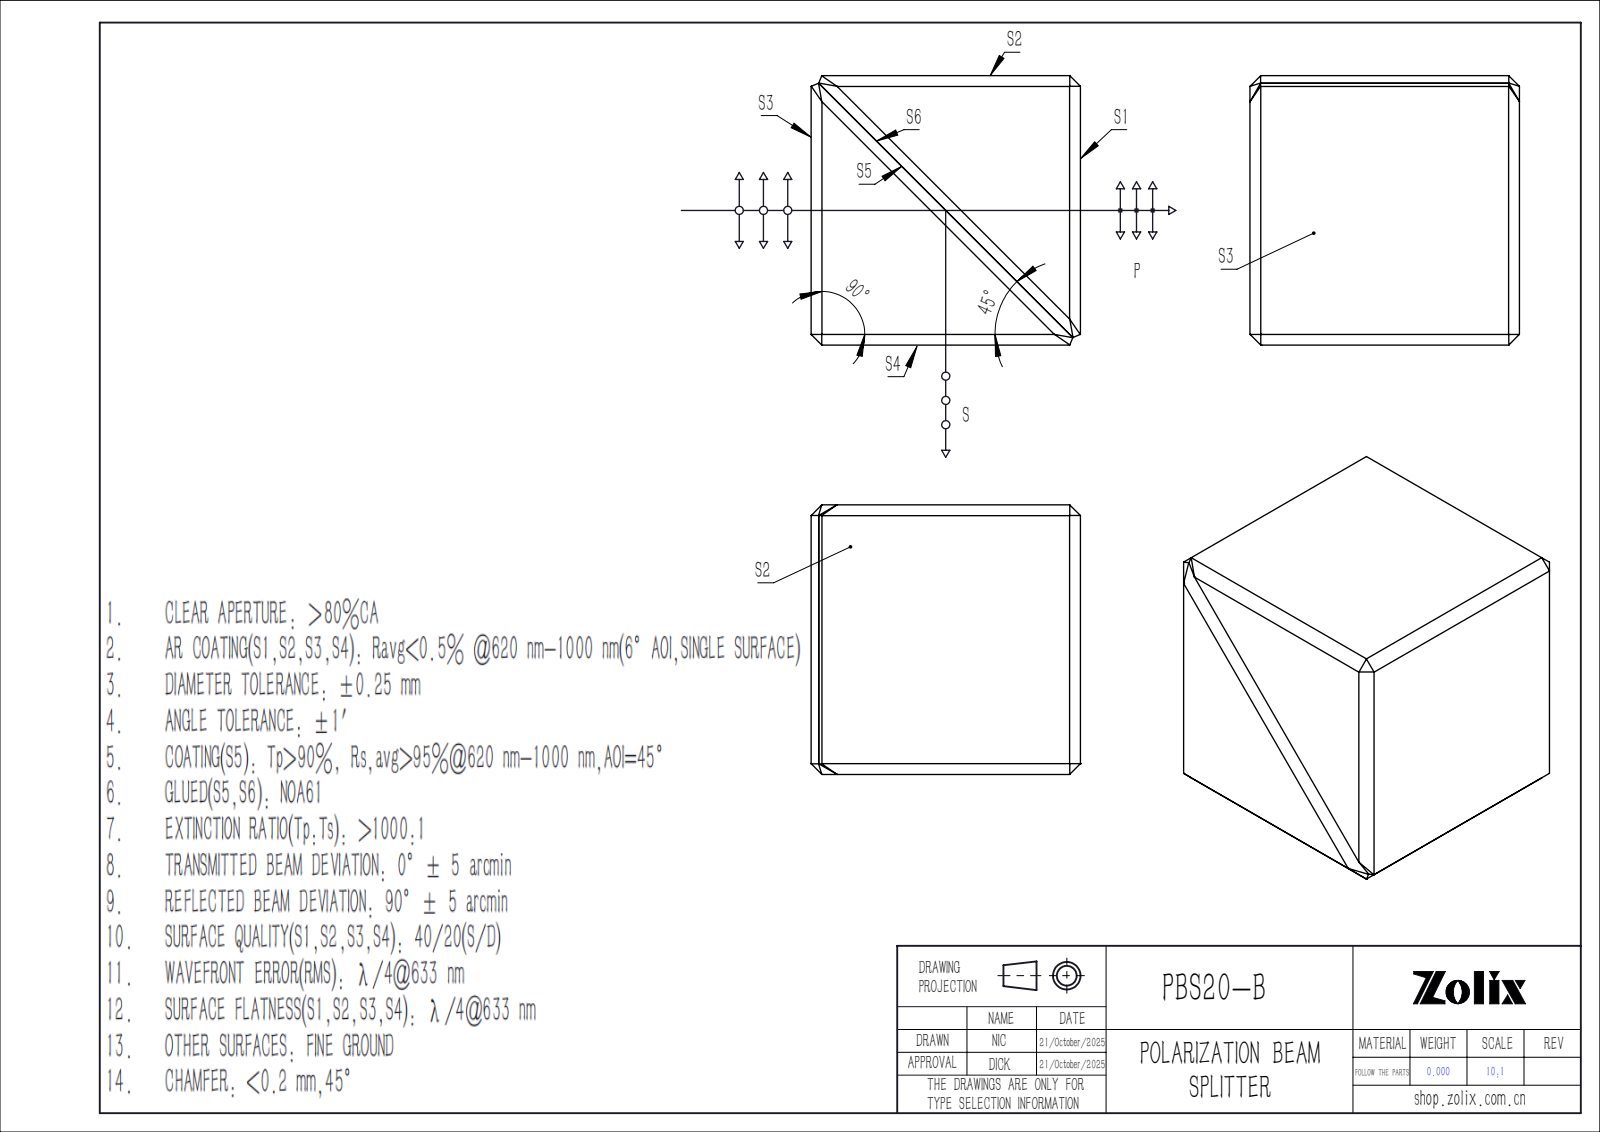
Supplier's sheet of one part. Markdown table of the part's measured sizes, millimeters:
| quantity | value |
| --- | --- |
| part name | PBS632-1-2; PBS632-1; PBS632-1-1 |
| STEP written by | SolidWorks 2022 (CONFIG_CONTROL_DESIGN) |
| units | millimeters |
| bodies | 2 solids, 43 faces (41 planar, 2 cylindrical, 0 other) |
| overall size | 20 × 20 × 20 |
| volume | 7 993 mm³ |
| surface area | 3 476 mm² |
| round holes (diameter × count) | 0.4 × 1 |
| main face-to-face distances | 20, 28, 13.86, 25.77, 13.99, 27.99, 14, 0.8, 19.2, 29.92 |
